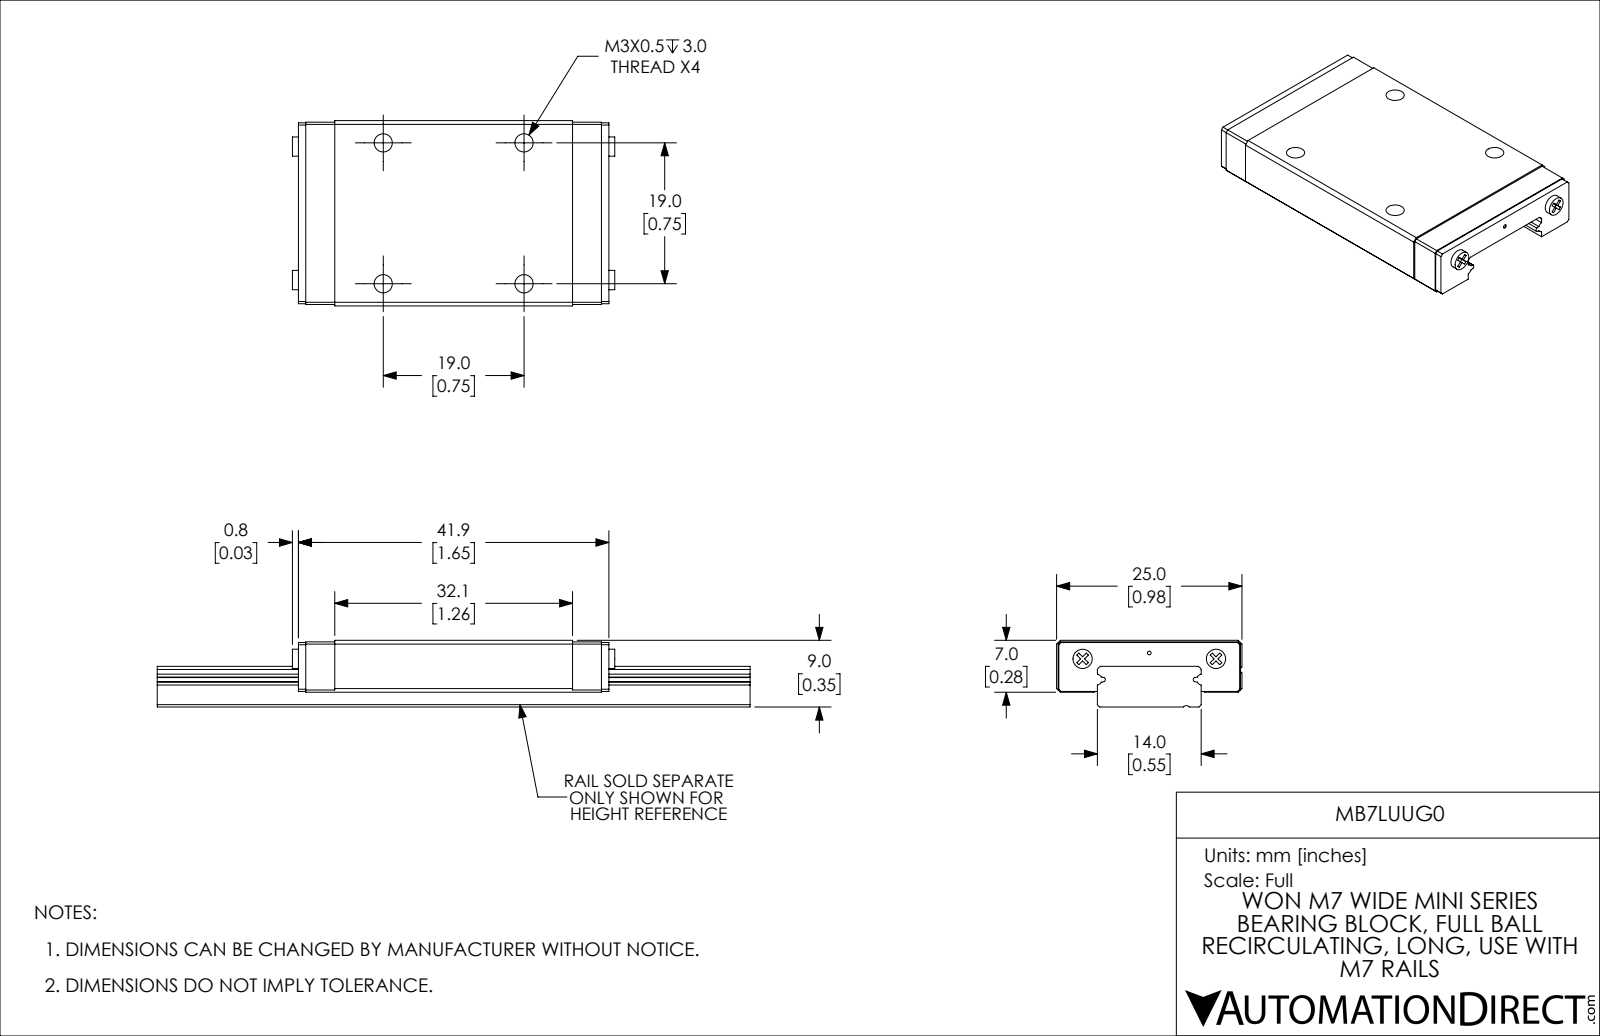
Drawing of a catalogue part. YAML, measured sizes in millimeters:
part_name: "MB7LUUG0"
step_written_by: "SolidWorks 2019 (CONFIG_CONTROL_DESIGN)"
units: millimeters
bodies: {solids: 1, faces: 150, planar: 113, cylindrical: 29, other: 8}
overall_size: [43.5, 25, 7]
volume: 5204
surface_area: 3408
round_holes:
  - {diameter: 2.46, count: 4}
  - {diameter: 0.5, count: 1}
round_bosses_or_shafts:
  - {diameter: 2.6, count: 2}
partial_cylinders:
  - {radius: 0.32, count: 2}
  - {radius: 0.75, count: 2}
  - {radius: 0.95, count: 2}
  - {radius: 0.5, count: 1}
face_to_face_distances: [3.5, 7, 6.8, 3.3, 25, 5.5, 19.5, 41.9, 24.8, 5.3]
hole_center_spacings: [19, 26.87]
